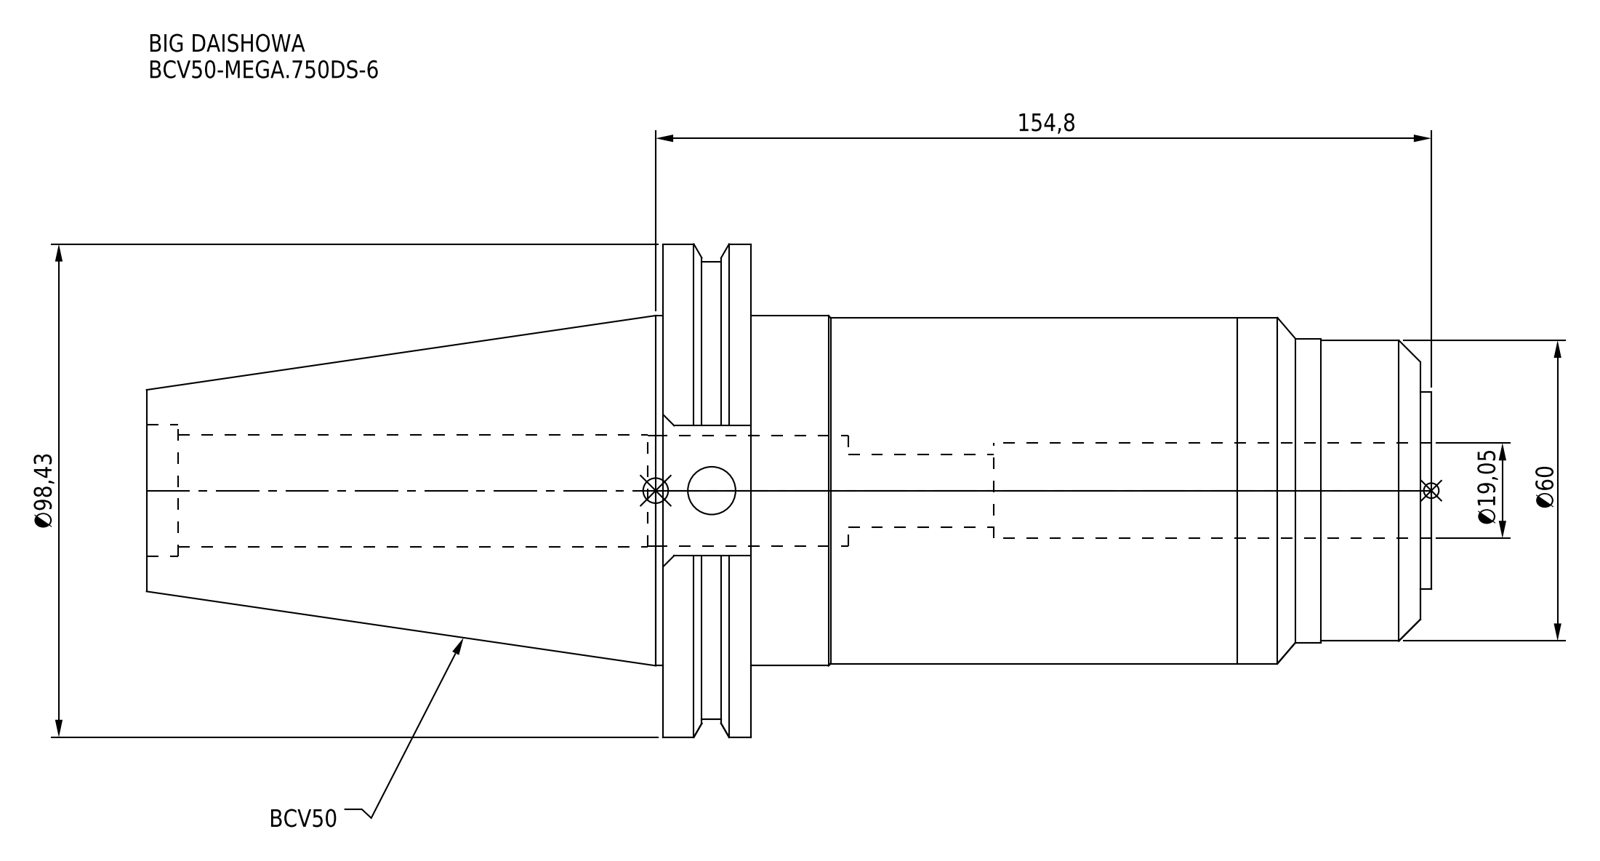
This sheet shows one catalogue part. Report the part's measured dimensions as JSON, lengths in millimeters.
{"part_name": "BCV50-MEGA_750DS-6", "step_written_by": "CREO PARAMETRIC BY PTC INC, 2016380 (AUTOMOTIVE_DESIGN)", "units": "millimeters", "bodies": {"solids": 1, "faces": 69, "planar": 25, "cylindrical": 32, "other": 12}, "overall_size": [256.4, 98.42, 94.95], "volume_mm3": 764102, "surface_area_mm2": 80178, "round_holes": [[9.53, 1], [14.5, 1], [19.05, 1], [22, 1], [22.3, 1], [26.23, 1]], "round_bosses_or_shafts": [[98.42, 1], [91.29, 1], [69.85, 1], [69, 1], [60.7, 1], [60, 1], [39.3, 1]], "face_to_face_distances": [17.55, 135.75, 153.3, 2.2, 133.55, 151.1, 256.4, 254.2, 120.65, 103.1]}
